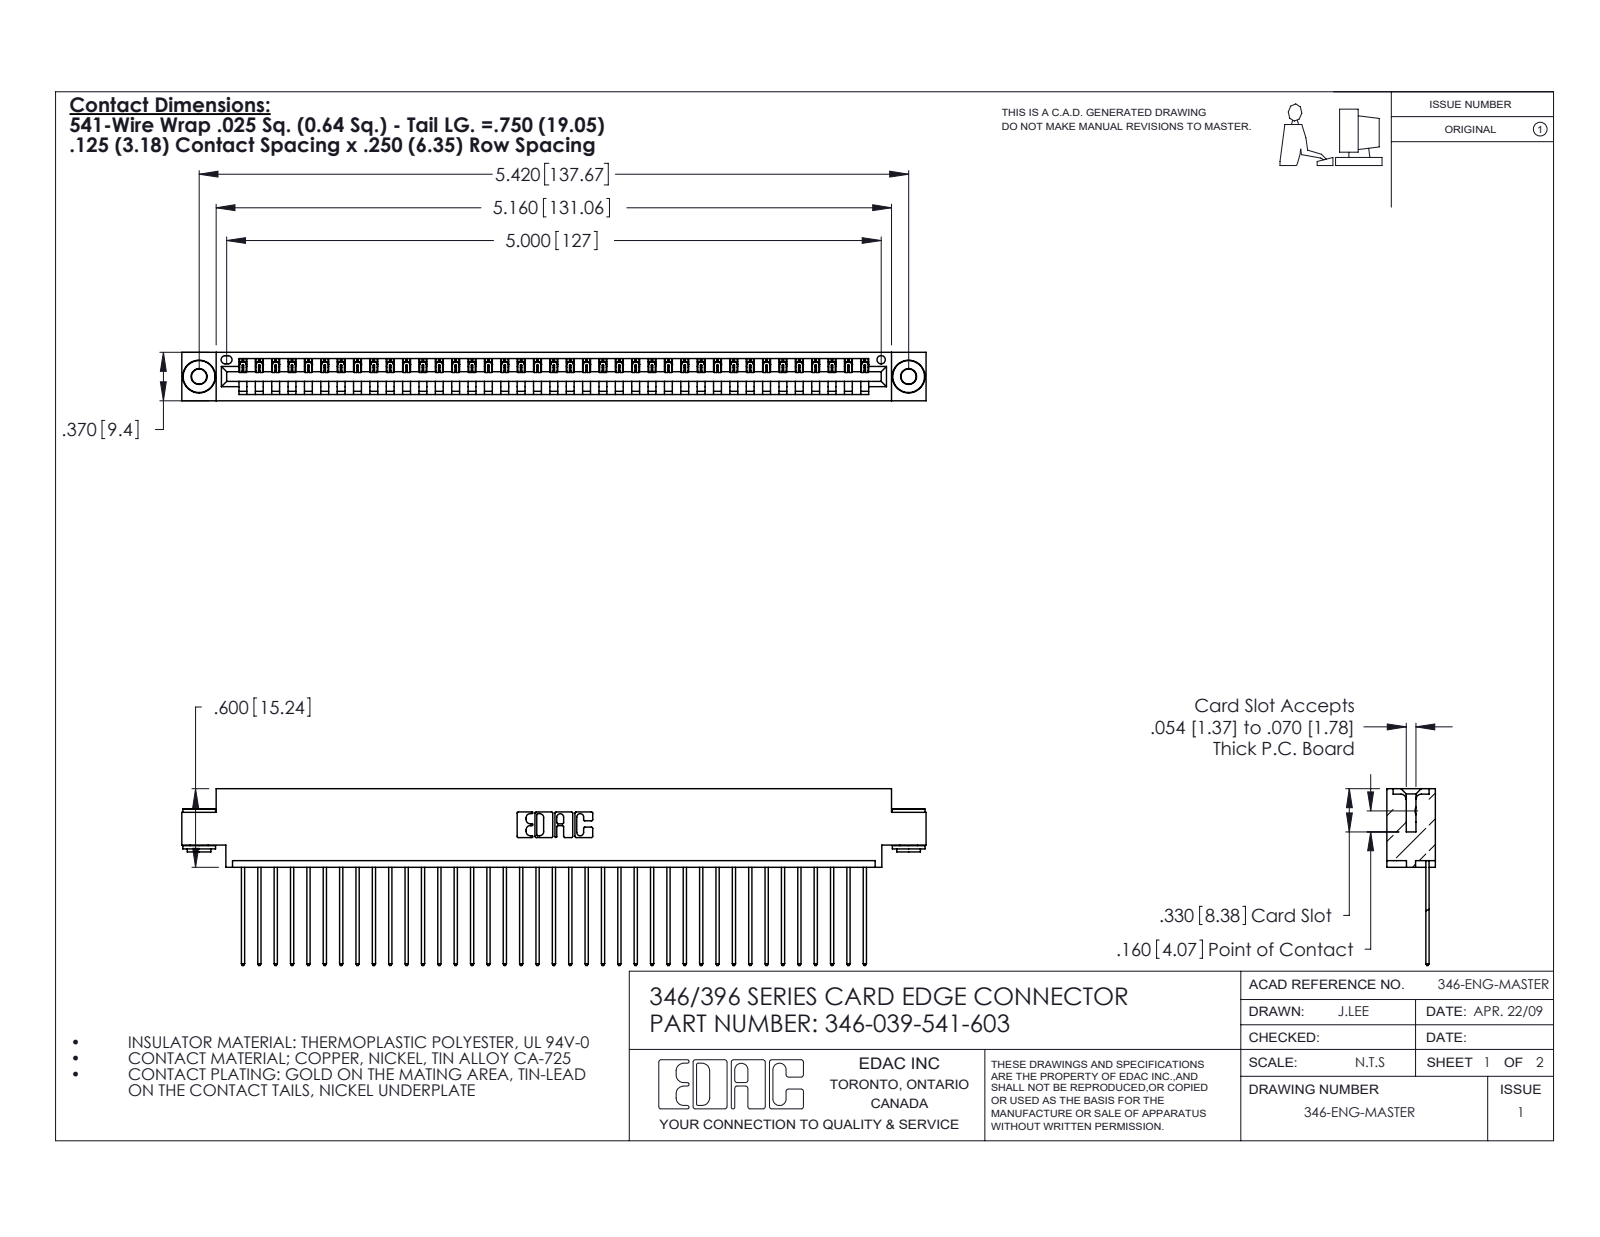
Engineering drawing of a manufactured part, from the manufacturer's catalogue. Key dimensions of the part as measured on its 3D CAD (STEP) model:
Part name (STEP PRODUCT): 346 Part_0.170 Offset - 0.156 Dia-TH; 345-292-001_345-293-141; 345-250-002_345-250-002-102; 346-039-541-603
STEP written by: SolidWorks 2020 (CONFIG_CONTROL_DESIGN)
Units: inches
Bodies: 42 solids, 2440 faces (1664 planar, 768 cylindrical, 8 other)
Overall size (bounding box): 5.685 × 1.35 × 0.37
Volume: 0.841 in³ · Surface area: 28.47 in²
Round holes (diameter × count): ⌀0.116 ×2, ⌀0.156 ×2, ⌀0.064 ×1
Round bosses / shafts (diameter × count): ⌀0.25 ×2, ⌀0.18 ×2, ⌀0.136 ×2
Partial cylindrical surfaces — rounded edges, fillets, slot ends (radius × count): R0.006 ×78, R0.01 ×78, R0.01 ×22, R0.007 ×6, R0.031 ×6, R0.026 ×3, R0.031 ×2, R0.04 ×2
Main face-to-face distances: 0.048, 0.322, 0.37, 0.25, 0.025, 0.072, 0.298, 0.222, 0.148, 0.1
Hole centre spacings: 0.246, 5.211, 5.42
